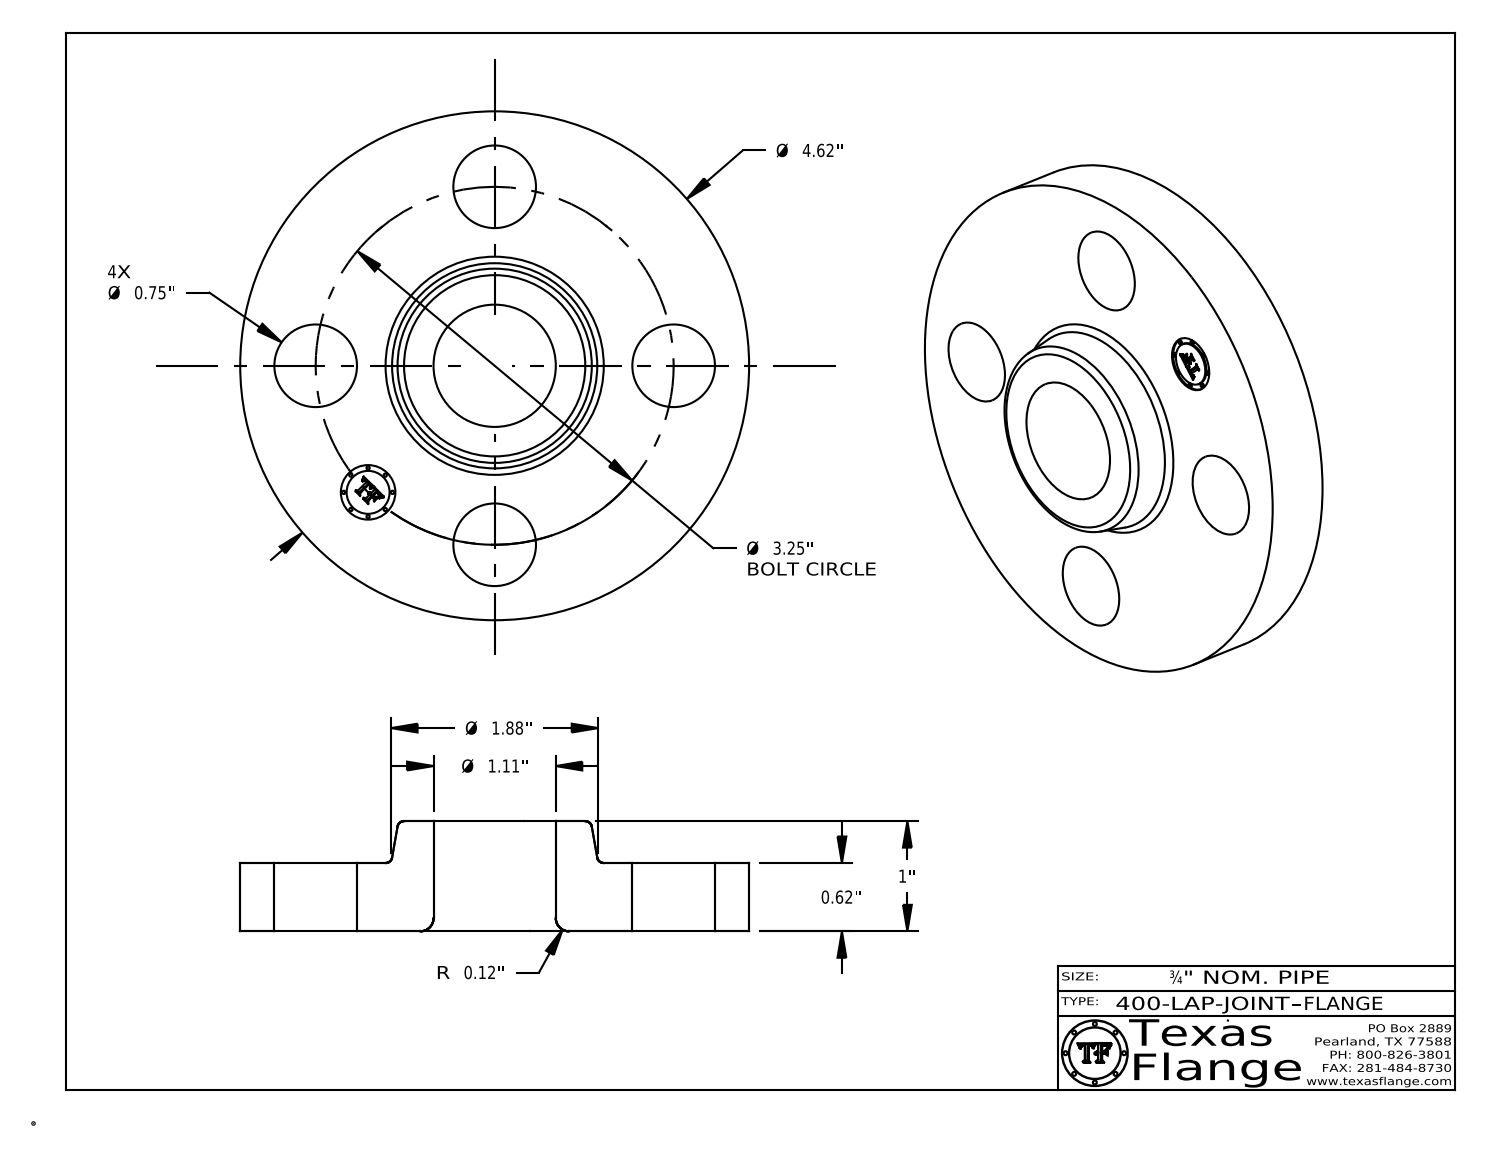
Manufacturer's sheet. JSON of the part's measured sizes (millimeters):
{"part_name": "400-LAP-JOINT FLANGE", "step_written_by": "CATIA V5 STEP AP214 (AUTOMOTIVE_DESIGN)", "units": "millimeters", "bodies": {"solids": 1, "faces": 408, "planar": 368, "cylindrical": 32, "other": 8}, "overall_size": [117.3, 117.3, 25.4], "volume_mm3": 152400, "surface_area_mm2": 30920, "round_holes": [[19.1, 4], [12.6, 1], [28.2, 1]], "round_bosses_or_shafts": [[0.8, 8], [117.3, 1], [9.9, 1]], "face_to_face_distances": [15.7, 25.4, 9.7, 15.4, 0.4, 10, 3.8, 3.7, 0.7, 2.4], "hole_center_spacings": [41.3, 58.4, 31.6, 76.3, 82.6]}
